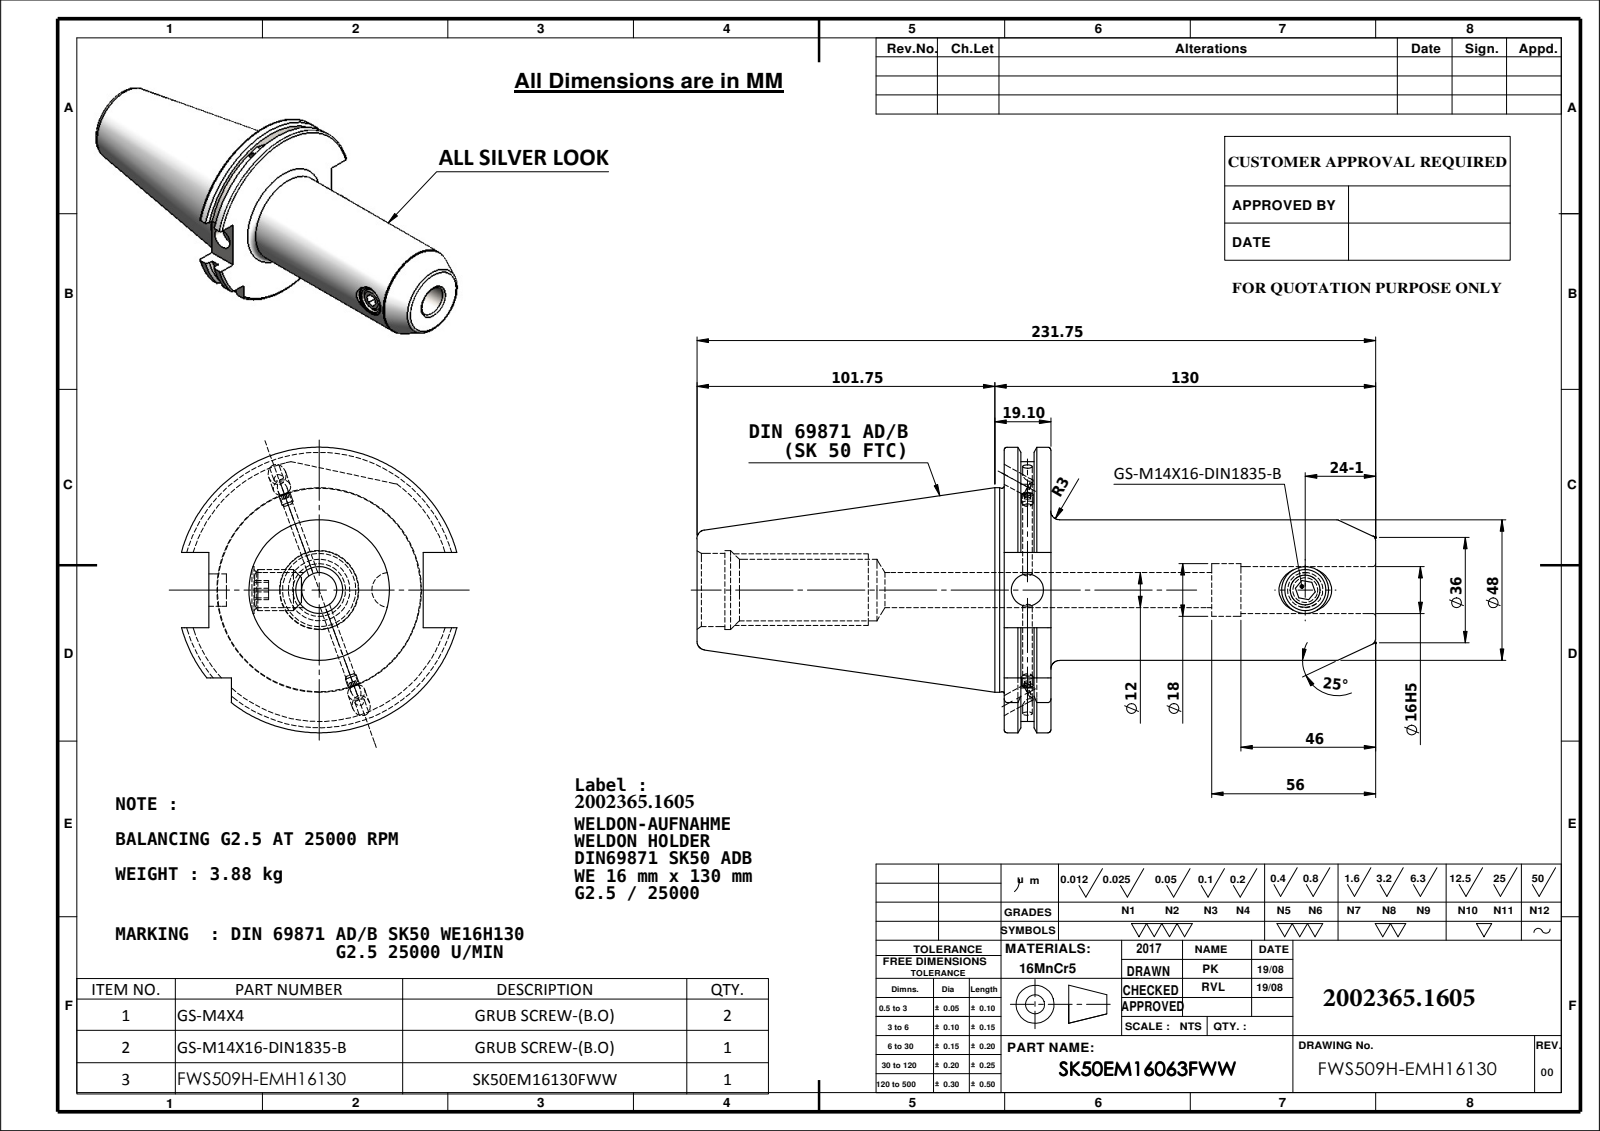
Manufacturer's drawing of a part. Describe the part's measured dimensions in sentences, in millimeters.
The part is named "SK50EM16130FWW; 91506-WE716130; M14X16_ISO 4026 - M12 x 12-N; Copy of M4X4_DIN 913 - M4 x 4-N". Its 3-D file was written by "SolidWorks 2009 (CONFIG_CONTROL_DESIGN)". It is 4 solids with 168 faces: 53 planar, 55 cylindrical and 60 other. Overall it measures 231.75 by 97.5 by 94.05 millimeters. Its volume is 508 583 cubic millimeters and its surface area 65 937 square millimeters. Round holes: 2 of diameter 6, 2 of diameter 12, 2 of diameter 16, 1 of diameter 3.3, 1 of diameter 11, 1 of diameter 18, 1 of diameter 21, 1 of diameter 25, 1 of diameter 27. Round bosses or shafts: 2 of diameter 4, 1 of diameter 69.85, 1 of diameter 69.45, 1 of diameter 48, 1 of diameter 14. Partial cylindrical surfaces (rounded edges, fillets, slot ends): 1 of radius 44.9, 1 of radius 48.75. The main face-to-face distances are 15.9, 126.8, 110.9, 5.66, 10.24, 121.14, 10.15, 4.49, 5.75, 116.65. The hole center spacings are 94.9.
